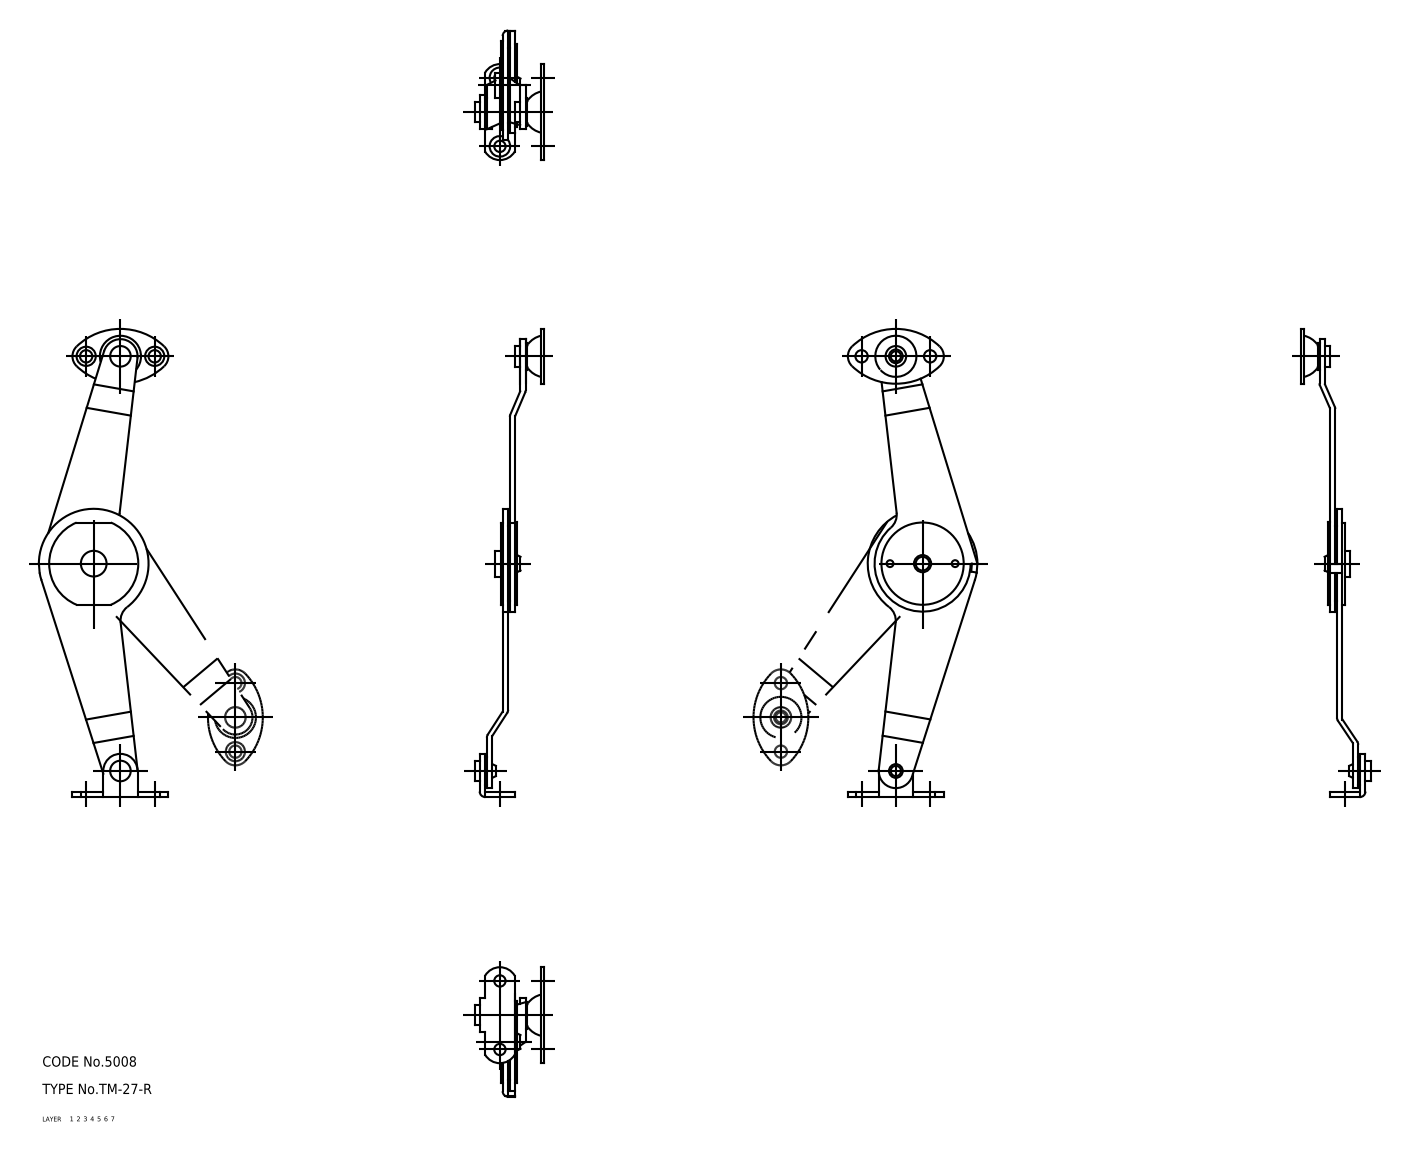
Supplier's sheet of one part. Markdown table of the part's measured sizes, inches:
| quantity | value |
| --- | --- |
| part name | rivet_A1_mr; rivet_A2_mr; washer_2_mr-1; ball_mr-1 (+8 more) |
| STEP written by | CADfix (AUTOMOTIVE_DESIGN) |
| units | inches |
| bodies | 13 solids, 155 faces (0 planar, 0 cylindrical, 155 other) |
| overall size | 5.378 × 1.488 × 0.803 |
| volume | 0.398 in³ |
| surface area | 16.5 in² |
